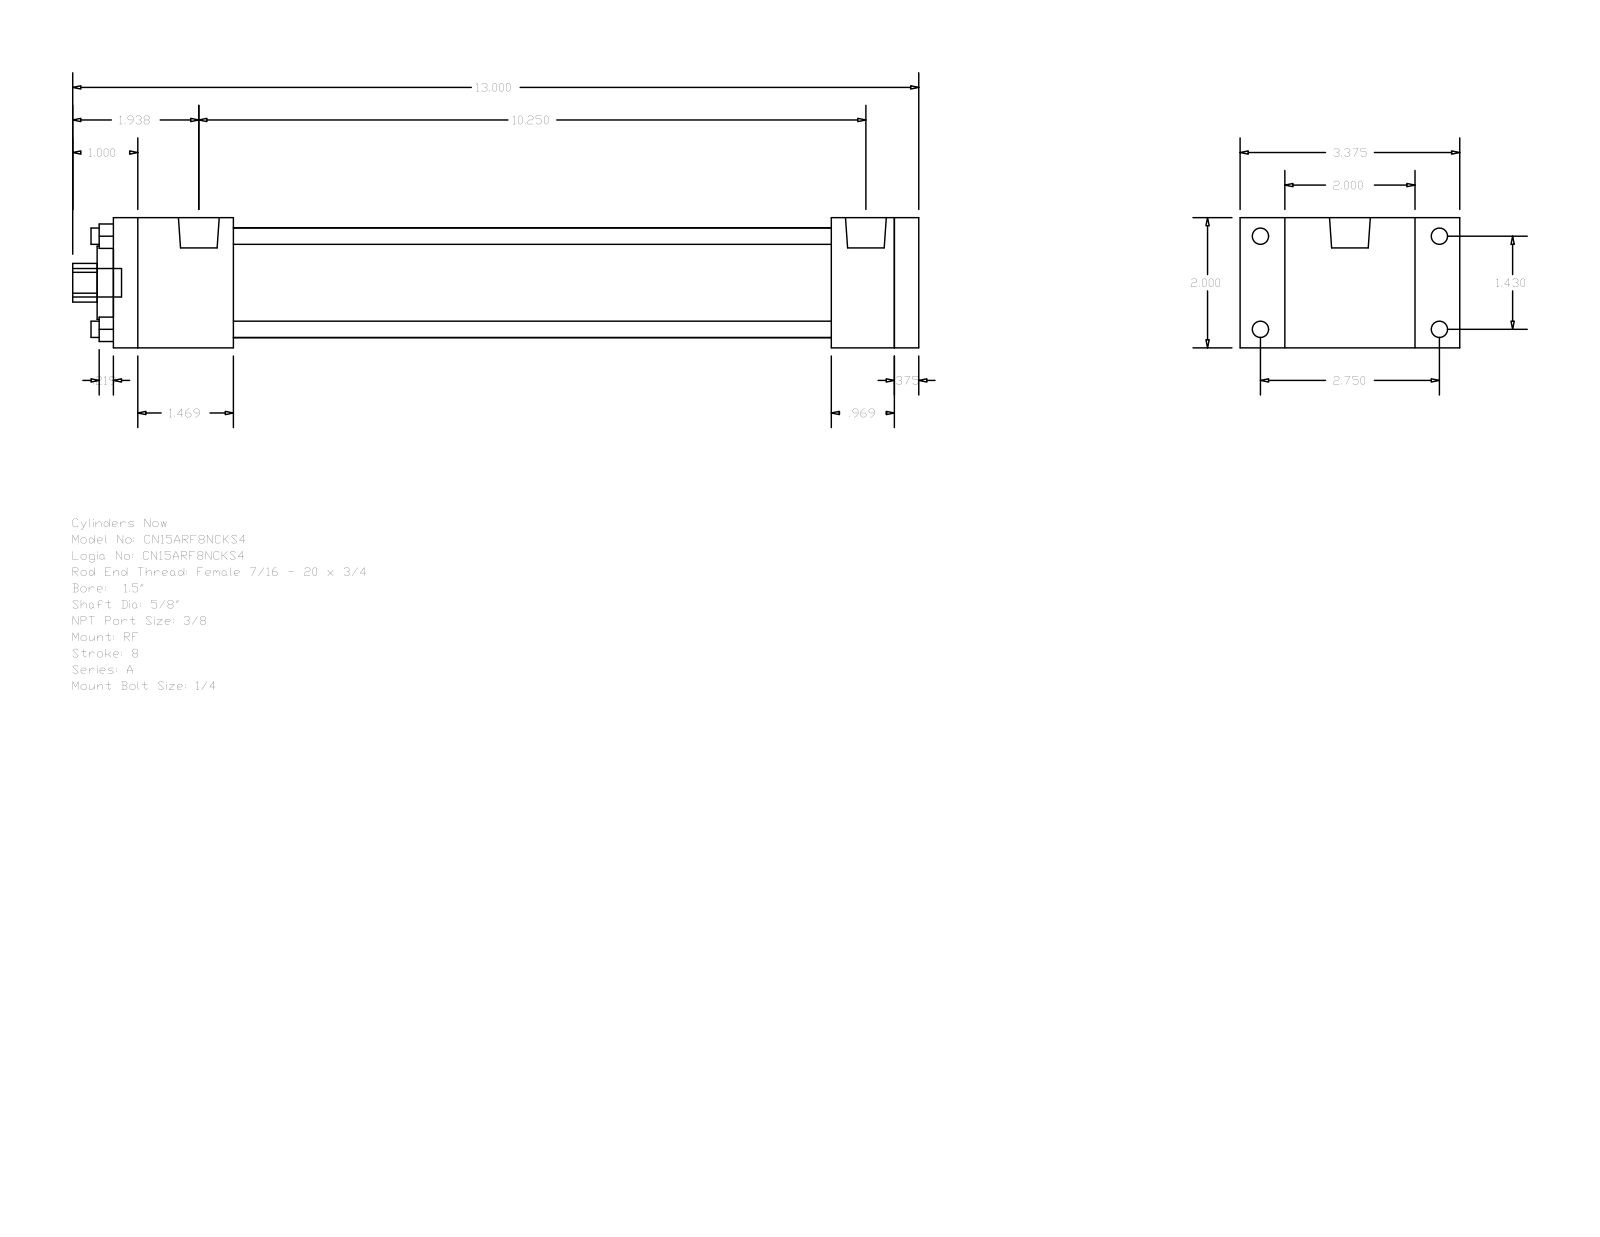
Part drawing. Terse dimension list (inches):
name: A_RF__0150_0.625
written by: GSSL Pune (CONFIG_CONTROL_DESIGN)
unit: in
bodies: 0 solids, 92 faces (64 planar, 28 cylindrical, 0 other)
size: 13 × 3.375 × 2
holes: 4× ⌀0.25, 1× ⌀0.625, 1× ⌀1.125, 1× ⌀1.69
bosses: 4× ⌀0.25, 4× ⌀0.219, 2× ⌀0.627, 1× ⌀0.437
rounds: 1× R0.297
face distances: 2, 0.375, 12, 12.375, 11.031, 0.969, 1.344, 1.844, 9.187, 10.156
hole spacings: 1.011, 1.43, 2.022
